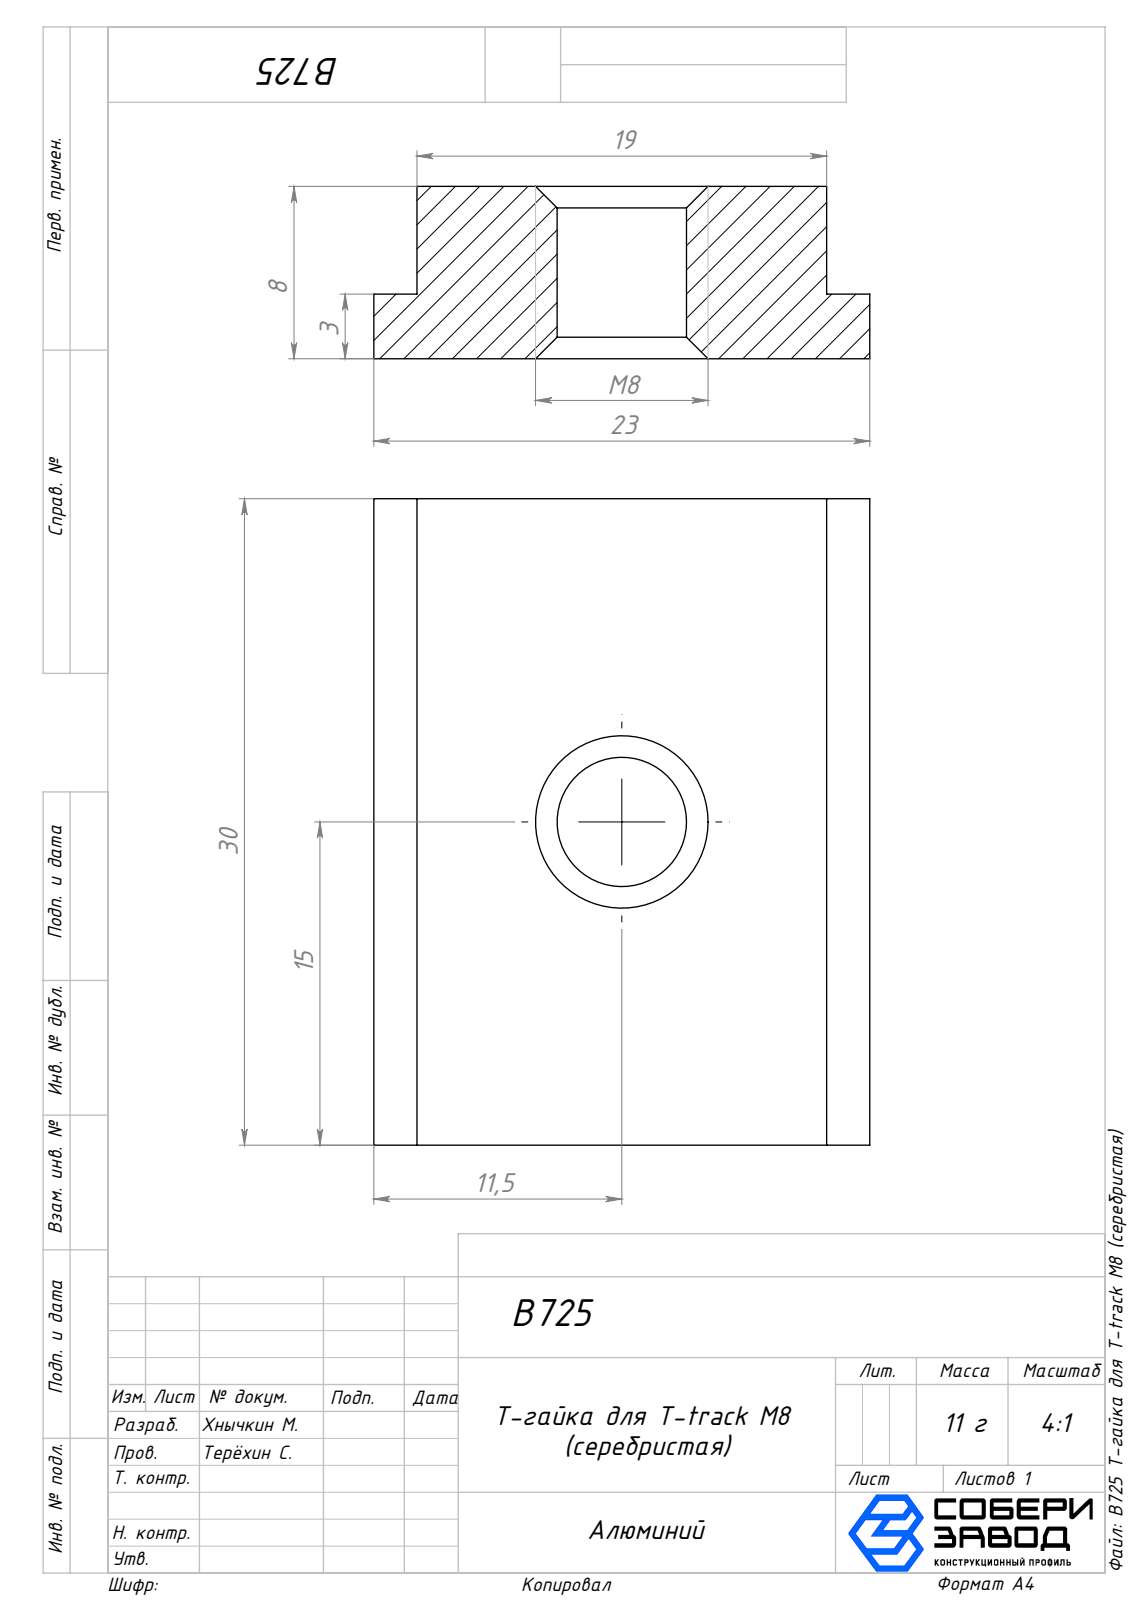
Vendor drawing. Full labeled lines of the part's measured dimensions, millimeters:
Part name (STEP PRODUCT): B725 Т-гайка для T-track M8 (серебристая)
STEP written by: SolidWorks 2025 (AUTOMOTIVE_DESIGN)
Units: millimetres
Bodies: 1 solid, 16 faces (10 planar, 2 cylindrical, 4 other)
Overall size (bounding box): 30 × 23 × 8
Volume: 4 673 mm³ · Surface area: 2 263 mm²
Round holes (diameter × count): ⌀6 ×1
Main face-to-face distances: 8, 2, 21, 30, 19, 3, 5, 23
